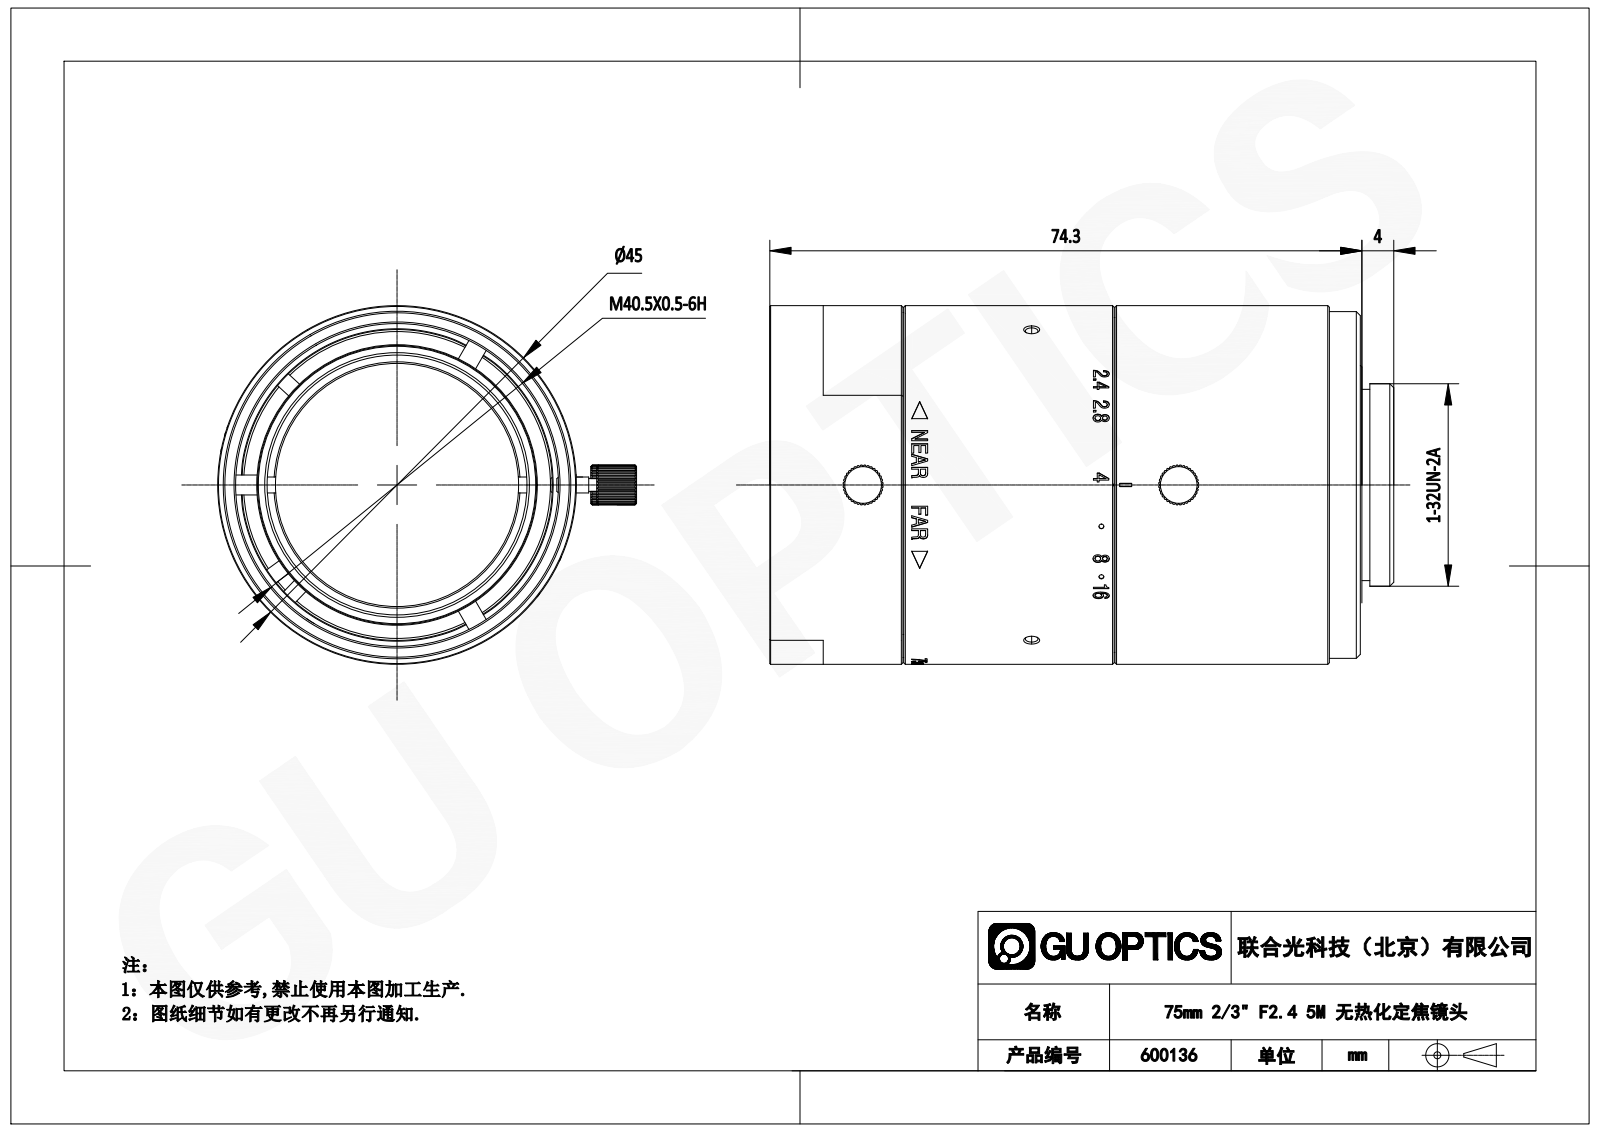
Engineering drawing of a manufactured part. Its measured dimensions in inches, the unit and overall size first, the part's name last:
Units: inches
Overall size (bounding box): 3.283 × 2.069 × 1.772
Round holes (diameter × count): ⌀0.079 ×15, ⌀0.063 ×7, ⌀0.043 ×3, ⌀0.051 ×3, ⌀0.055 ×3, ⌀0.059 ×3, ⌀0.071 ×3, ⌀0.098 ×3, ⌀0.126 ×3, ⌀0.61 ×1, ⌀0.657 ×1, ⌀0.709 ×1
Round bosses / shafts (diameter × count): ⌀0.079 ×4, ⌀0.067 ×3, ⌀0.063 ×2, ⌀1.772 ×1, ⌀1.764 ×1, ⌀1.713 ×1, ⌀1.705 ×1, ⌀1.693 ×1
Partial cylindrical surfaces — rounded edges, fillets, slot ends (radius × count): R0.049 ×12, R0.039 ×9, R0.059 ×2, R0.098 ×2
Main face-to-face distances: 0.078, 0.02, 1.331, 0.086, 0.659, 0.581, 0.435, 1.017, 1.094, 0.303
Hole centre spacings: 0.396, 0.436, 0.669, 0.726, 0.833, 1.123, 1.159, 1.559
Bodies: 0 solids, 1868 faces (604 planar, 439 cylindrical, 825 other)
Part name (STEP PRODUCT): 600136
STEP written by: SolidWorks 2020 (CONFIG_CONTROL_DESIGN)
